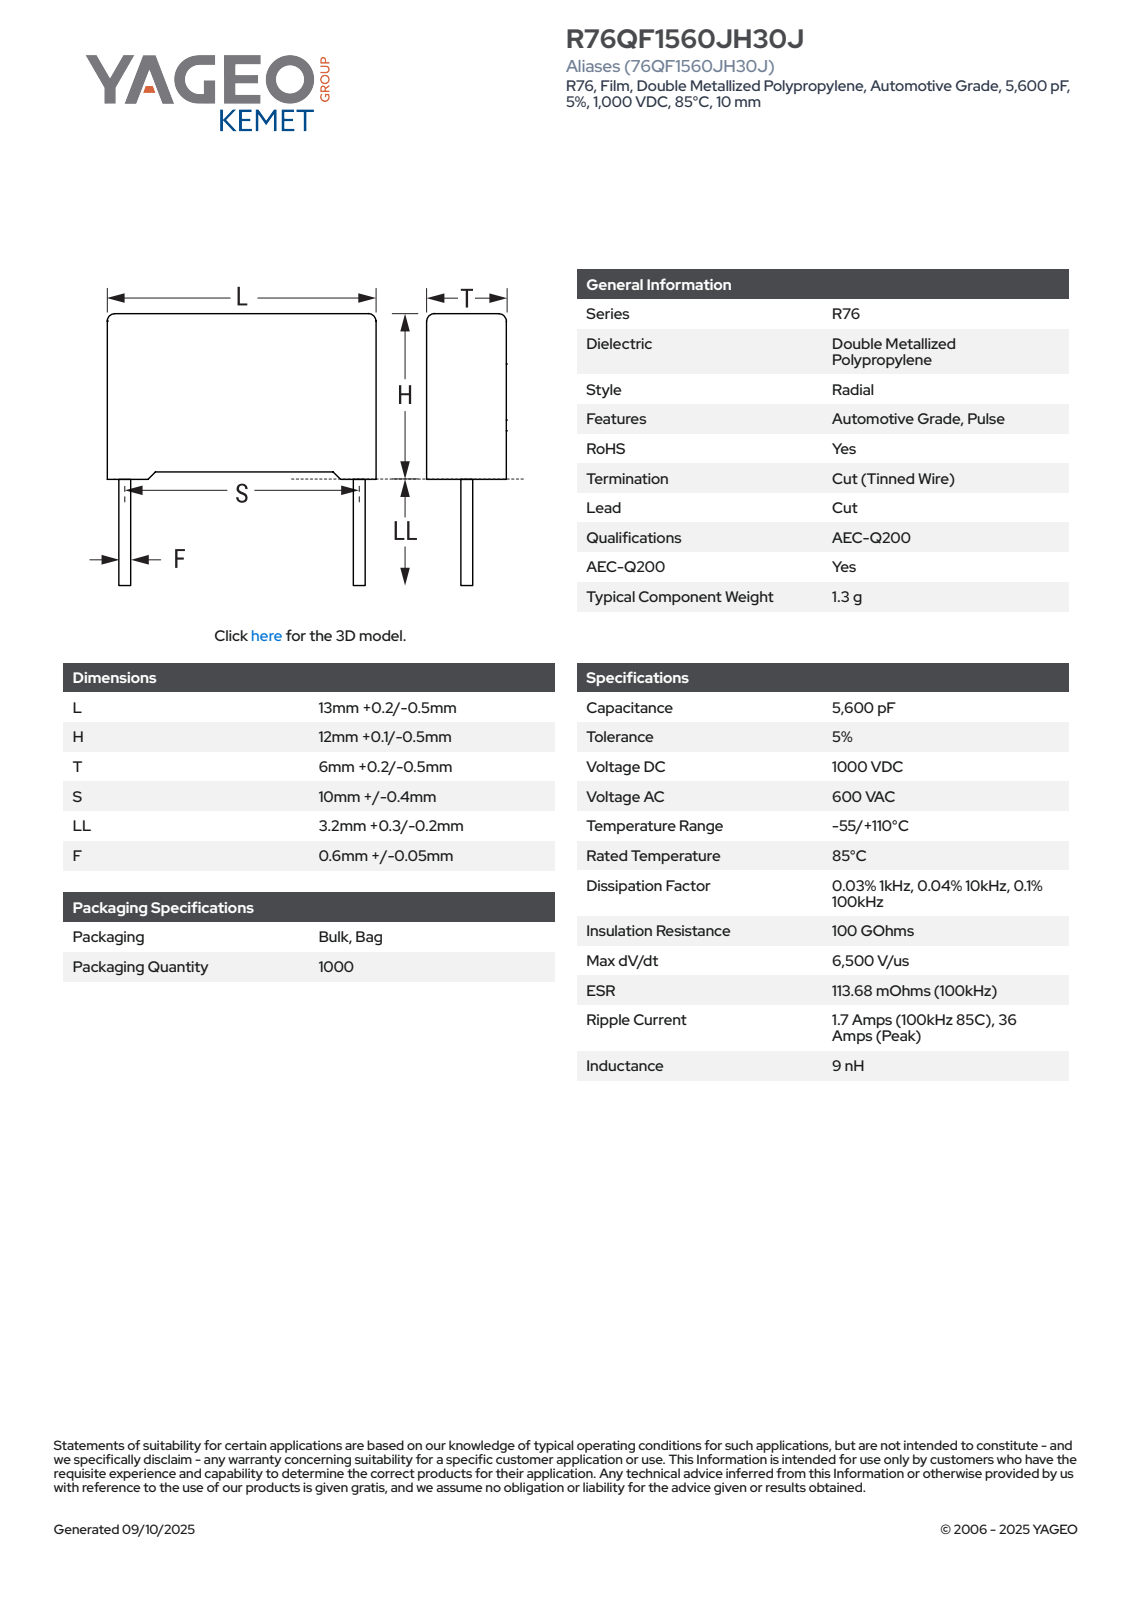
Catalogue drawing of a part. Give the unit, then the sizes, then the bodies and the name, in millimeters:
Units: millimetres
Overall size (bounding box): 15.6 × 13.2 × 6.21
Round bosses / shafts (diameter × count): ⌀0.65 ×2
Partial cylindrical surfaces — rounded edges, fillets, slot ends (radius × count): R0.5 ×4
Main face-to-face distances: 6.2, 13.2, 11.35, 0.44, 5.76, 0.75, 12.1, 12.76, 5.32, 0.42
Volume: 939 mm³ · Surface area: 671 mm²
Bodies: 4 solids, 85 faces (77 planar, 8 cylindrical, 0 other)
Part name (STEP PRODUCT): CFR_RB2_13X12X6_L13.2H12.1T6.2S10LL3.5F0.65
STEP written by: SolidWorks 2021 (AUTOMOTIVE_DESIGN)
